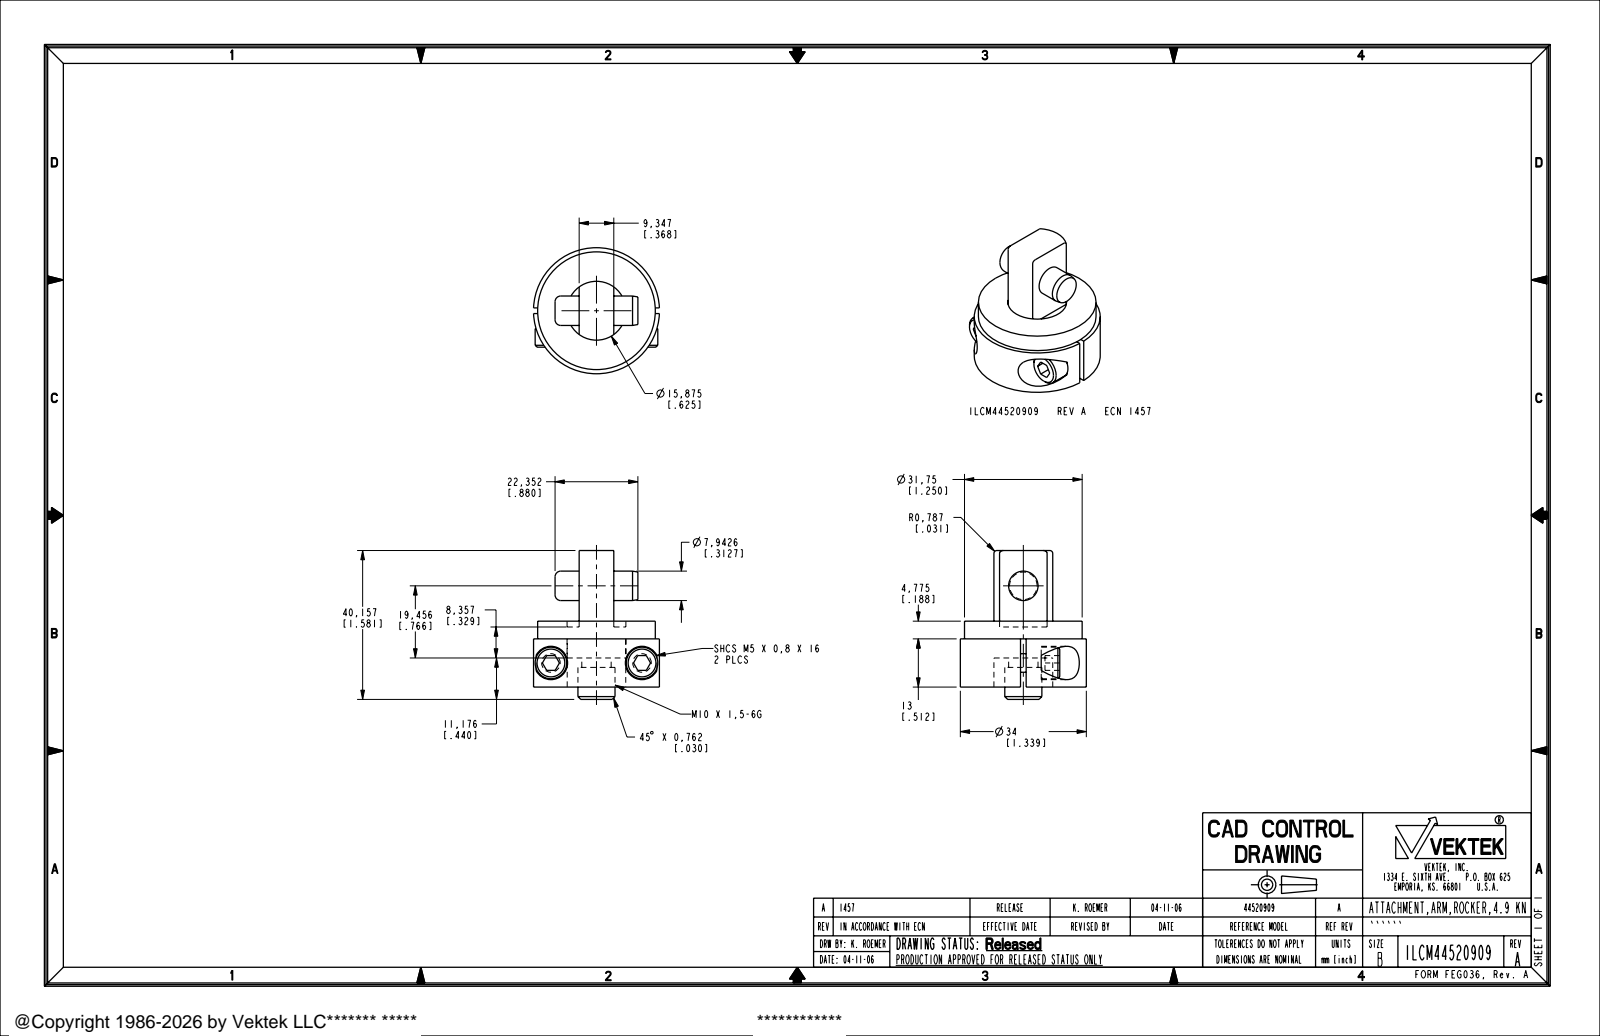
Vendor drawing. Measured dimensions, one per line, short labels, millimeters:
name: ILCM44520909
written by: PRO/ENGINEER BY PARAMETRIC TECHNOLOGY CORPORATION, 2004290 (AUTOMOTIVE_DESIGN_CC2)
unit: mm
bodies: 1 solid, 83 faces (41 planar, 30 cylindrical, 12 other)
size: 40.16 × 34 × 33.97
volume: 17 355 mm³; area: 6 710 mm²
holes: 2× ⌀8.99, 1× ⌀15.88
bosses: 2× ⌀8.51, 2× ⌀5, 1× ⌀34, 1× ⌀31.75, 1× ⌀10.01, 1× ⌀7.94, 1× ⌀7.92
face distances: 17.78, 9.34, 1.52, 7.85, 9.93, 13, 5.15, 4.78, 36.83, 28.98
hole spacings: 24.58
